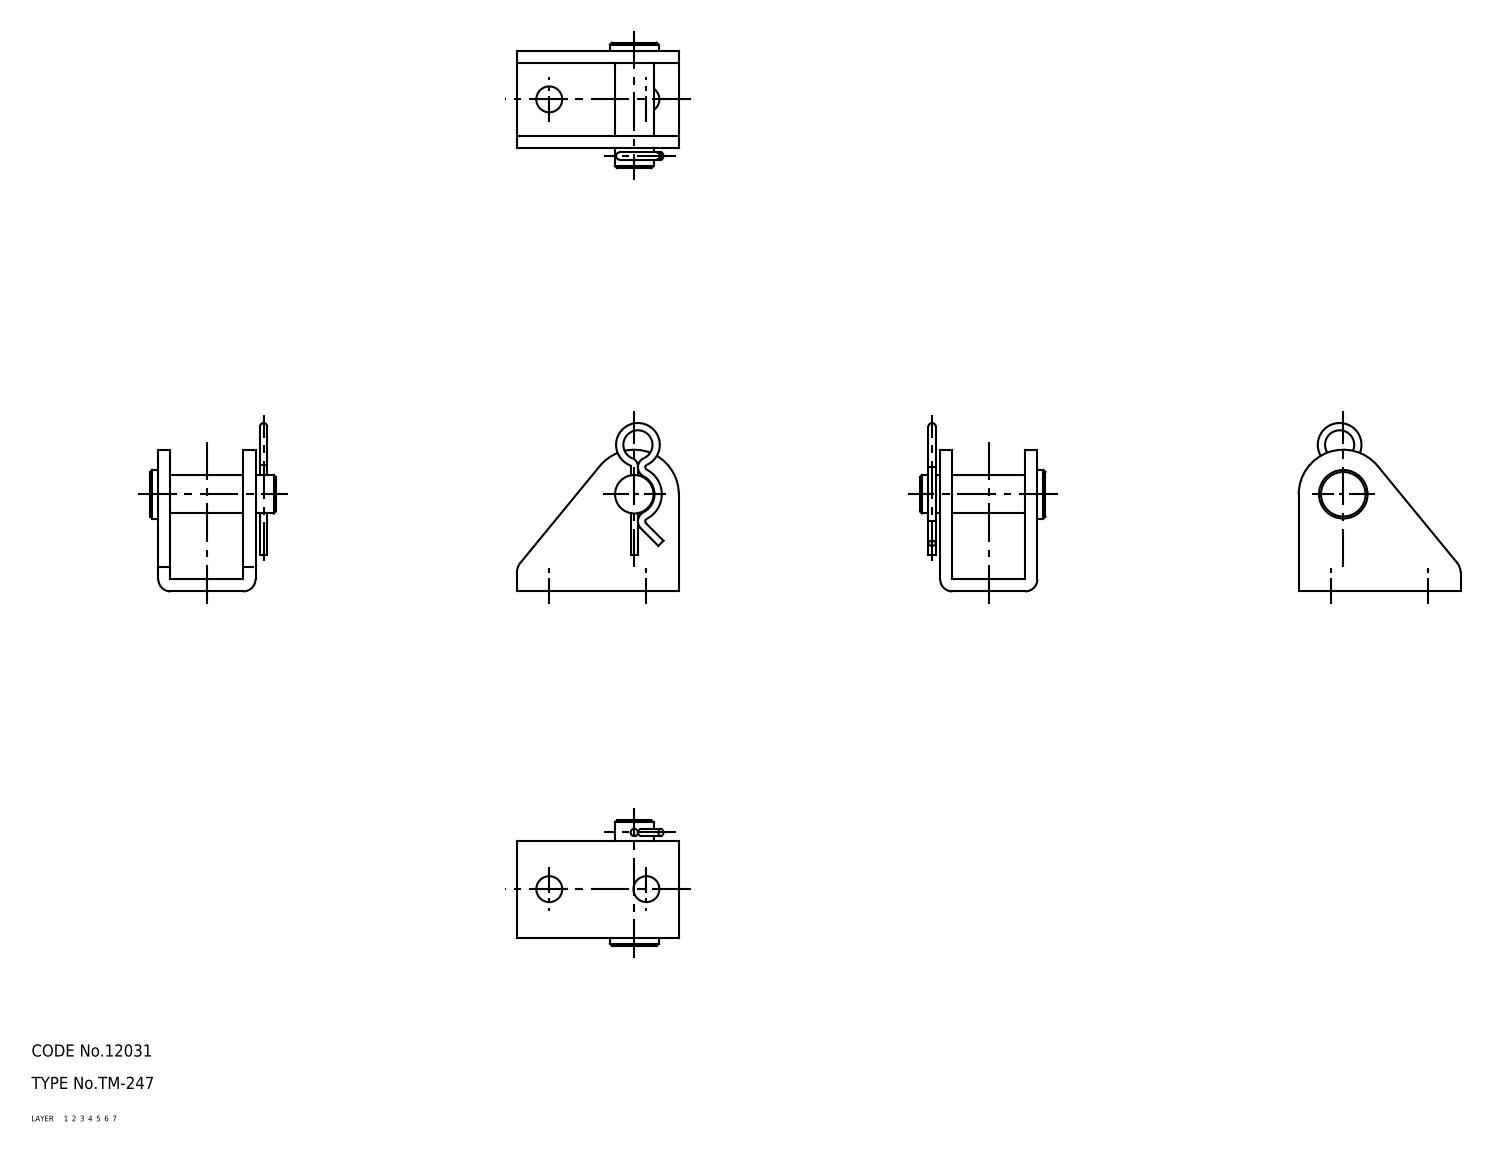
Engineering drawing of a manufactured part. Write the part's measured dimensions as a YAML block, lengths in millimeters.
part_name: "67112363"
step_written_by: "CADfix (AUTOMOTIVE_DESIGN)"
units: millimeters
bodies: {solids: 1, faces: 50, planar: 0, cylindrical: 0, other: 50}
overall_size: [41.6, 40, 31]
volume: 9977
surface_area: 7027
